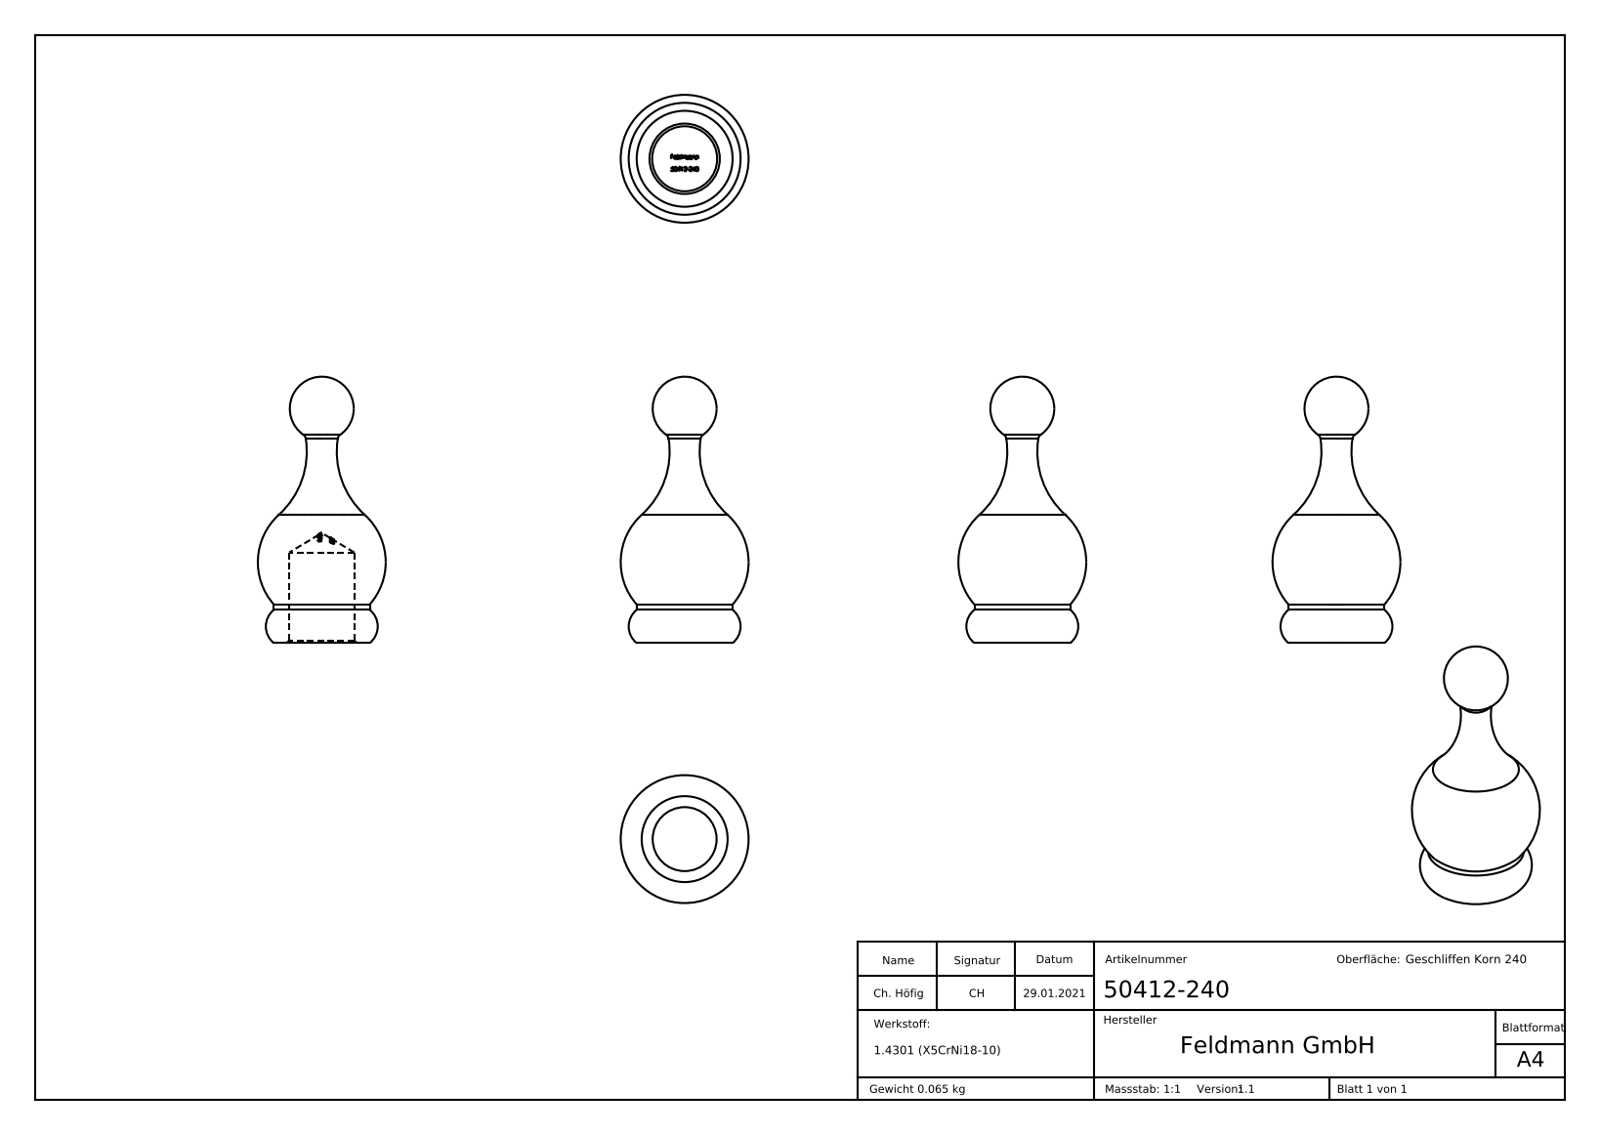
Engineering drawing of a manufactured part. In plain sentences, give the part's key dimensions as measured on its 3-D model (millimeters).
The part is named "50412-240". Its 3-D file was written by "SolidWorks 2018 (CONFIG_CONTROL_DESIGN)". It is 1 solid with 242 faces: 109 planar, 4 cylindrical and 129 other. Overall it measures 50 by 24 by 24 millimeters. Its volume is 8 241 cubic millimeters and its surface area 3 555 square millimeters. Round holes: 1 of diameter 12.2. Round bosses or shafts: 1 of diameter 18. The main face-to-face distances are 2.41, 2.33, 0.71, 0.4, 0.63, 1.78, 0.83, 2.24, 0.47, 0.36.
